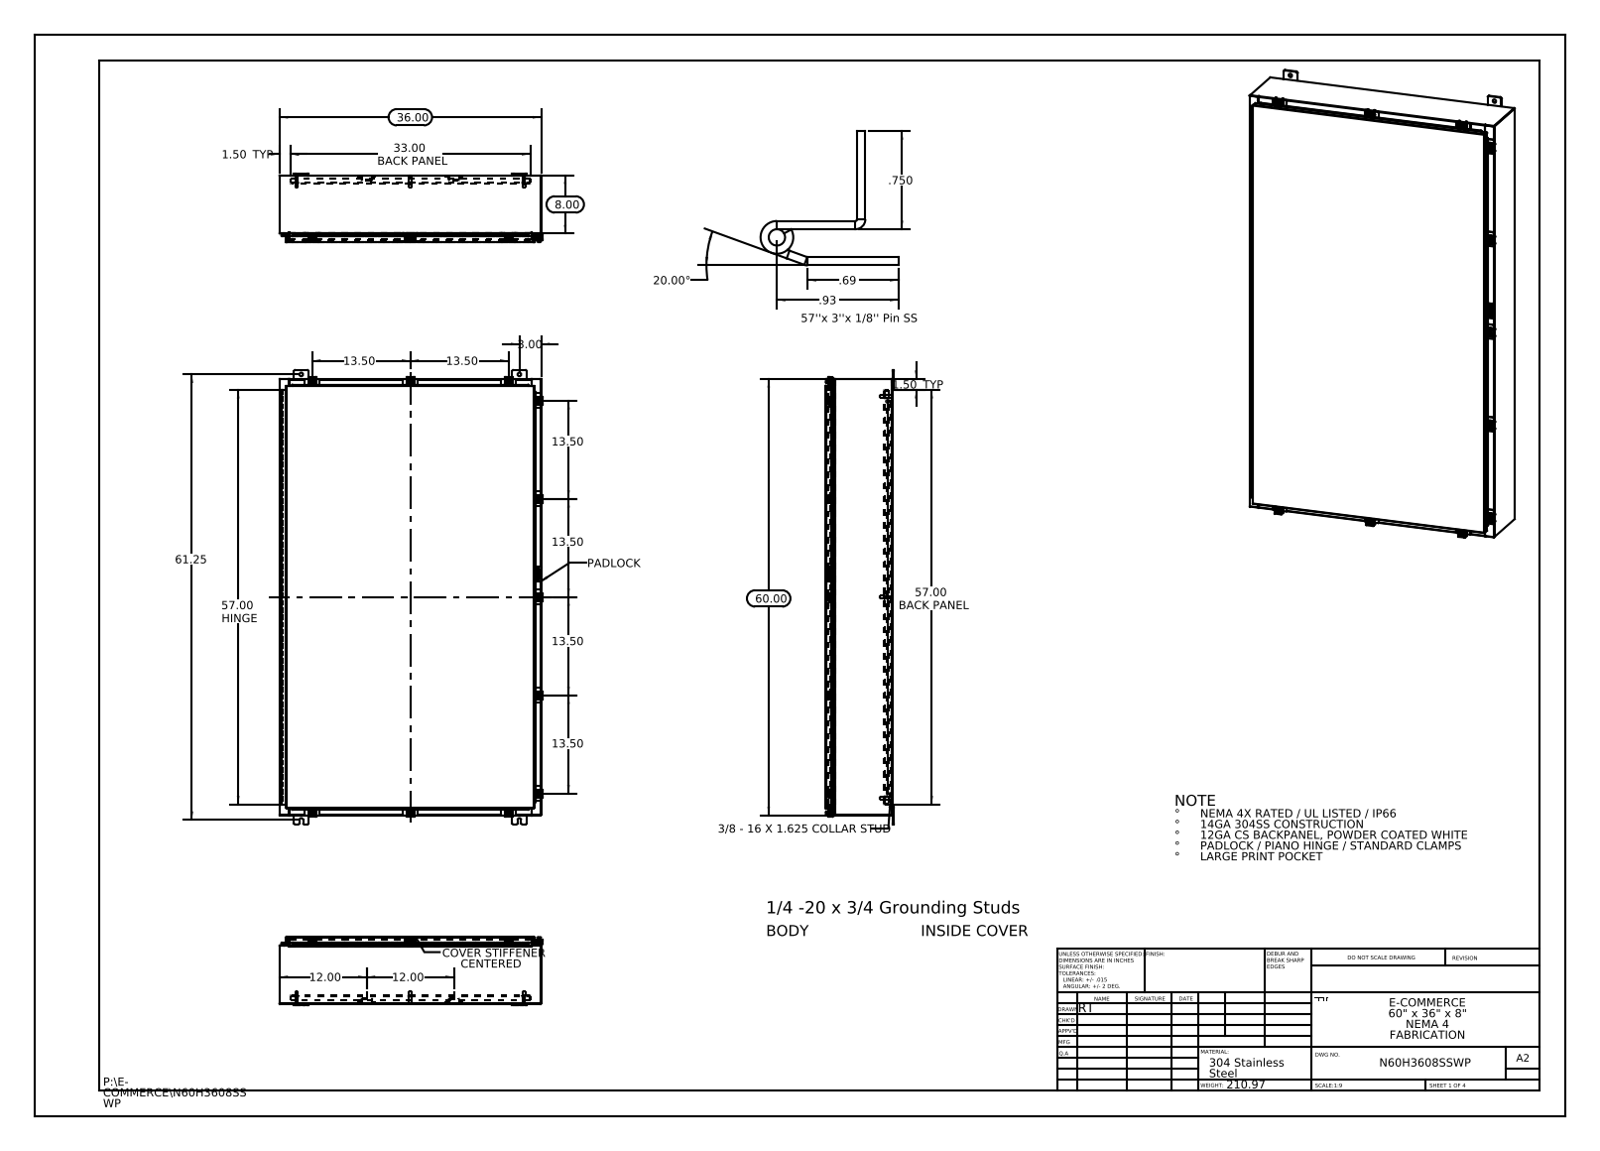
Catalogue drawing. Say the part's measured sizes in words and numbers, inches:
The part is named "N60H3608SSWP Backpanel; N60H3608SSWP Hinge Cover Side; N60H3608SSWP Bottom; N60H3608SSWP Mounting Feet (+8 more)". Its 3-D file was written by "SolidWorks 2013 (CONFIG_CONTROL_DESIGN)". It is 79 solids with 3408 faces: 1766 planar, 1466 cylindrical and 176 other. Overall it measures 62.5 by 36.211 by 9.389 inches. Its volume is 738.8 cubic inches and its surface area 18 317 square inches. Round holes: 12 of diameter 0.5, 11 of diameter 0.213, 11 of diameter 0.26, 8 of diameter 0.25, 2 of diameter 0.125, 1 of diameter 0.125. Round bosses or shafts: 12 of diameter 0.25, 11 of diameter 0.5, 11 of diameter 0.399, 8 of diameter 0.625, 8 of diameter 0.375, 8 of diameter 0.33. Partial cylindrical surfaces (rounded edges, fillets, slot ends): 50 of radius 0.06, 39 of radius 0.013, 33 of radius 0.088, 24 of radius 0.19, 22 of radius 0.12, 22 of radius 0.141, 17 of radius 0.05, 16 of radius 0.08. The main face-to-face distances are 0.075, 9.126, 9.051, 0.104, 9.201, 1, 8.126, 1.075, 8.051, 1.179. The hole center spacings are 13.5, 13.663, 2.225, 27, 27.625, 29.802, 41.709, 57.39.
